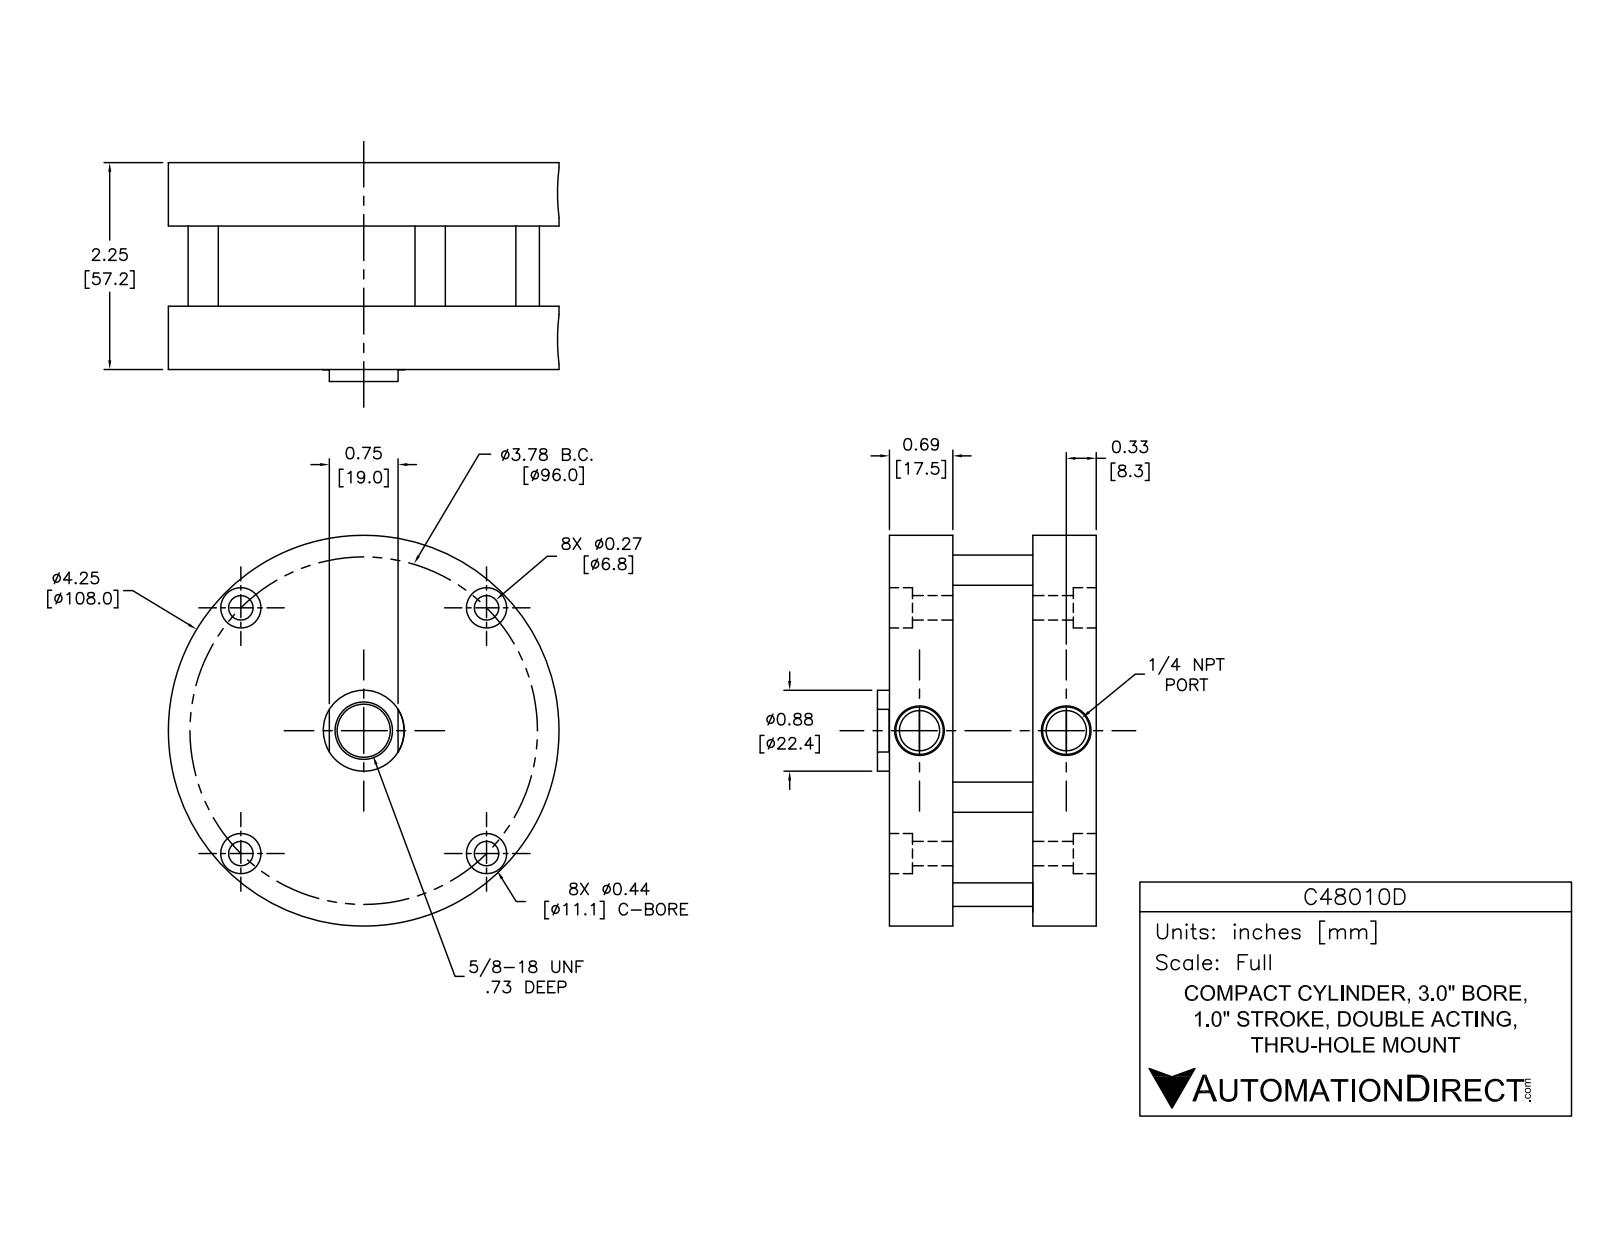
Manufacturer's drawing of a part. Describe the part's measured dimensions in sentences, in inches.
The part is named "C48010D-rod_part; C48010D-FO1_BM_heads (2); C48010D-FO1_BM_r; C48010D (+3 more)". Its 3-D file was written by "SolidWorks 2014 (AUTOMOTIVE_DESIGN)". It is 9 solids with 165 faces: 49 planar, 98 cylindrical and 18 other. Overall it measures 4.25 by 4.25 by 2.38 inches. Its volume is 19.56 cubic inches and its surface area 153.3 square inches. Round holes: 4 of diameter 0.225, 4 of diameter 0.281, 4 of diameter 0.406, 2 of diameter 0.218, 1 of diameter 0.565, 1 of diameter 0.88, 1 of diameter 0.882, 1 of diameter 3, 1 of diameter 3.125. Round bosses or shafts: 4 of diameter 0.45, 4 of diameter 0.225, 1 of diameter 4.25. The main face-to-face distances are 0.384, 1.866, 0.69, 1.56, 0.306, 1.176, 2.25, 1.482, 0.87, 0.866. The hole center spacings are 0.477, 1.89, 1.89, 2.314, 2.672, 2.673, 2.989, 3.75.
